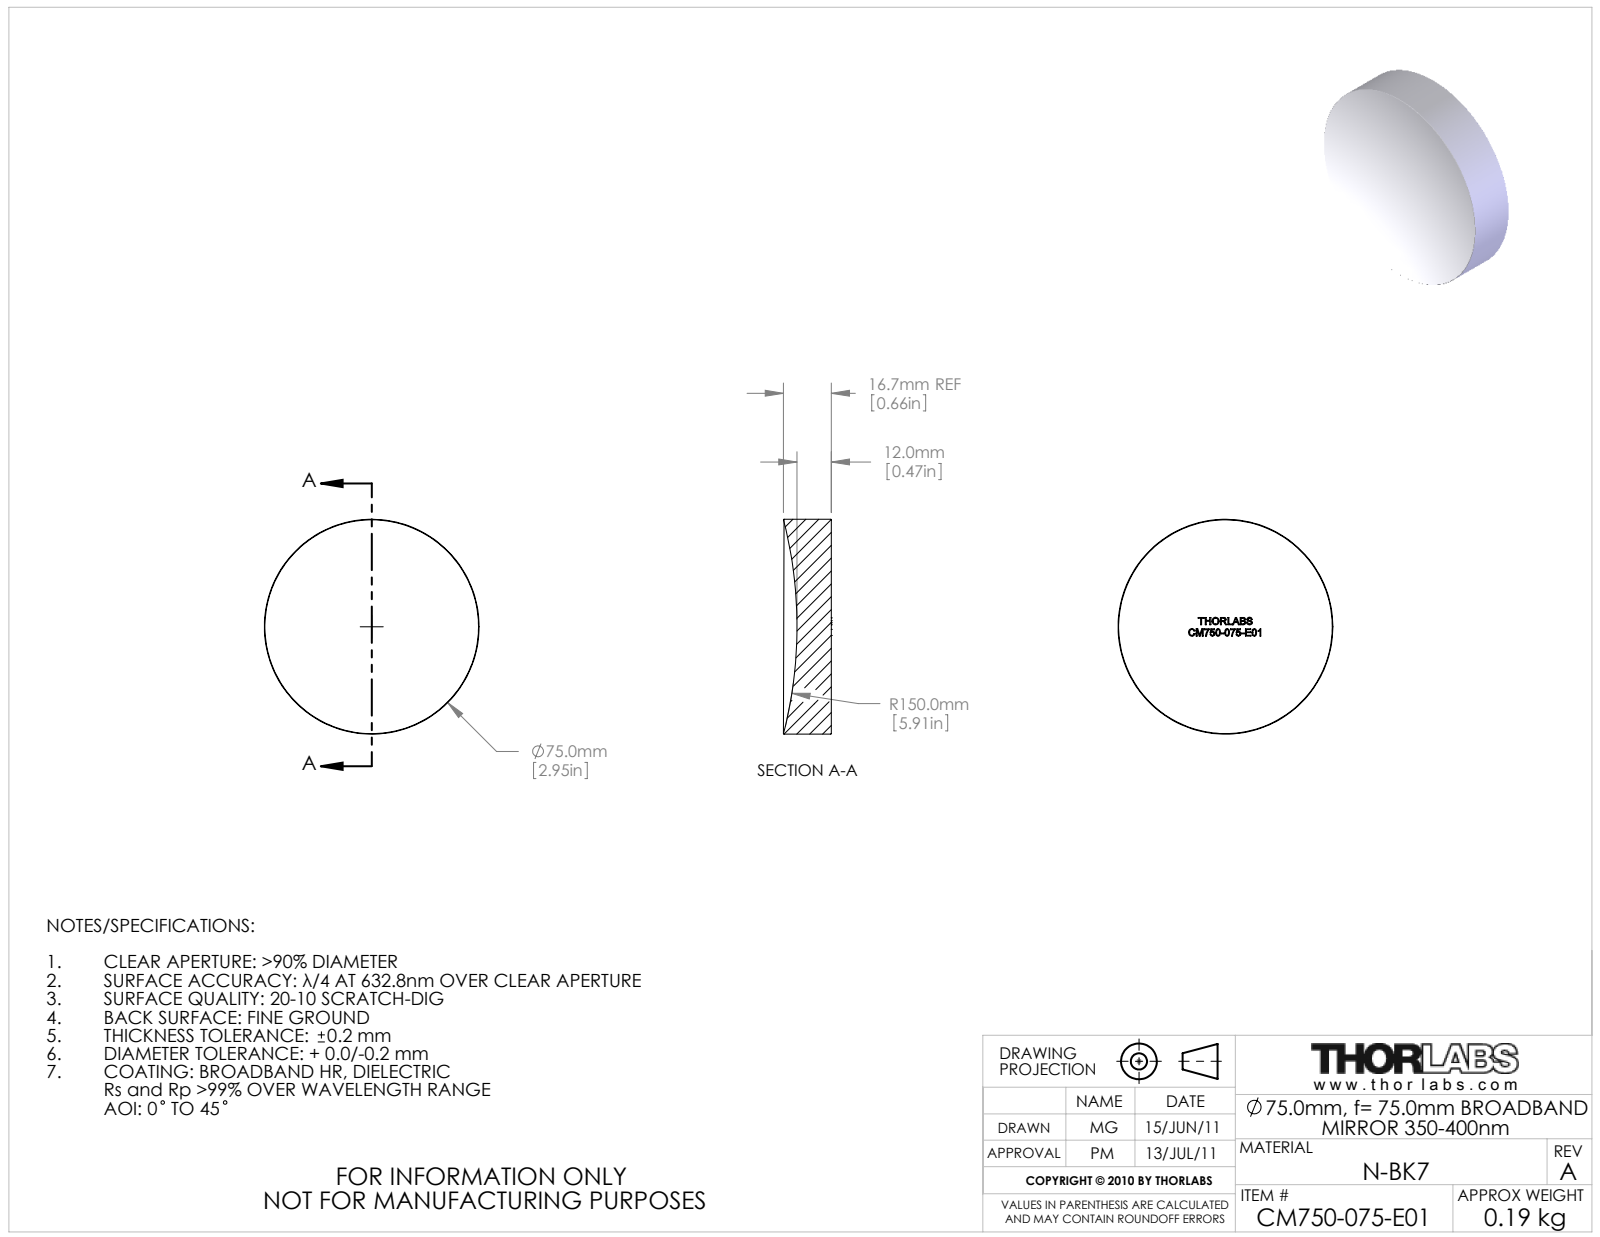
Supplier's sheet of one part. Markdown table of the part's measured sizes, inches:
| quantity | value |
| --- | --- |
| part name | 22619-E0W |
| STEP written by | SolidWorks 2011 (AUTOMOTIVE_DESIGN) |
| units | inches |
| bodies | 0 solids, 38 faces (30 planar, 2 cylindrical, 6 other) |
| overall size | 2.953 × 2.953 × 0.658 |
| round bosses / shafts (diameter × count) | 2.953 × 1 |
